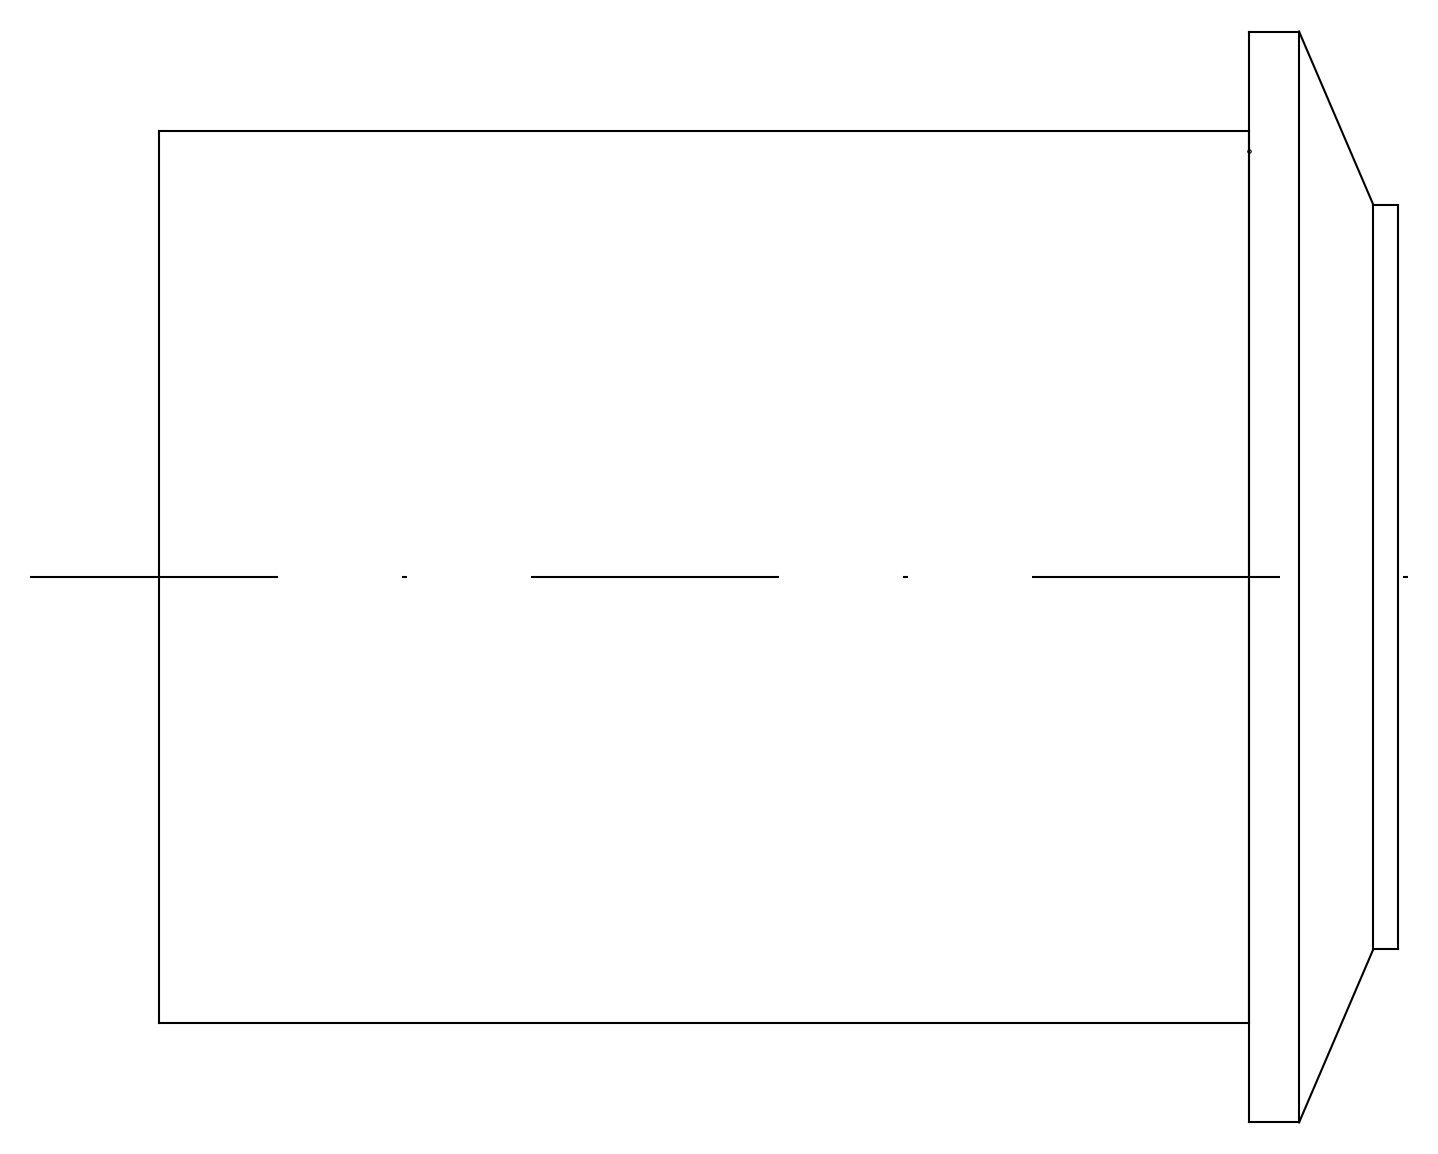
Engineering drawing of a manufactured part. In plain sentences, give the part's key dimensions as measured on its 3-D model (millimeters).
Its 3-D file was written by "THINKDESIGN (CONFIG_CONTROL_DESIGN)". It is 1 solid with 7 faces: 3 planar, 3 cylindrical and 1 other. Overall it measures 25 by 22 by 22 millimeters. Its volume is 6 474 cubic millimeters and its surface area 2 115 square millimeters. Round bosses or shafts: 1 of diameter 22, 1 of diameter 18, 1 of diameter 15. The main face-to-face distances are 25, 22, 3.
